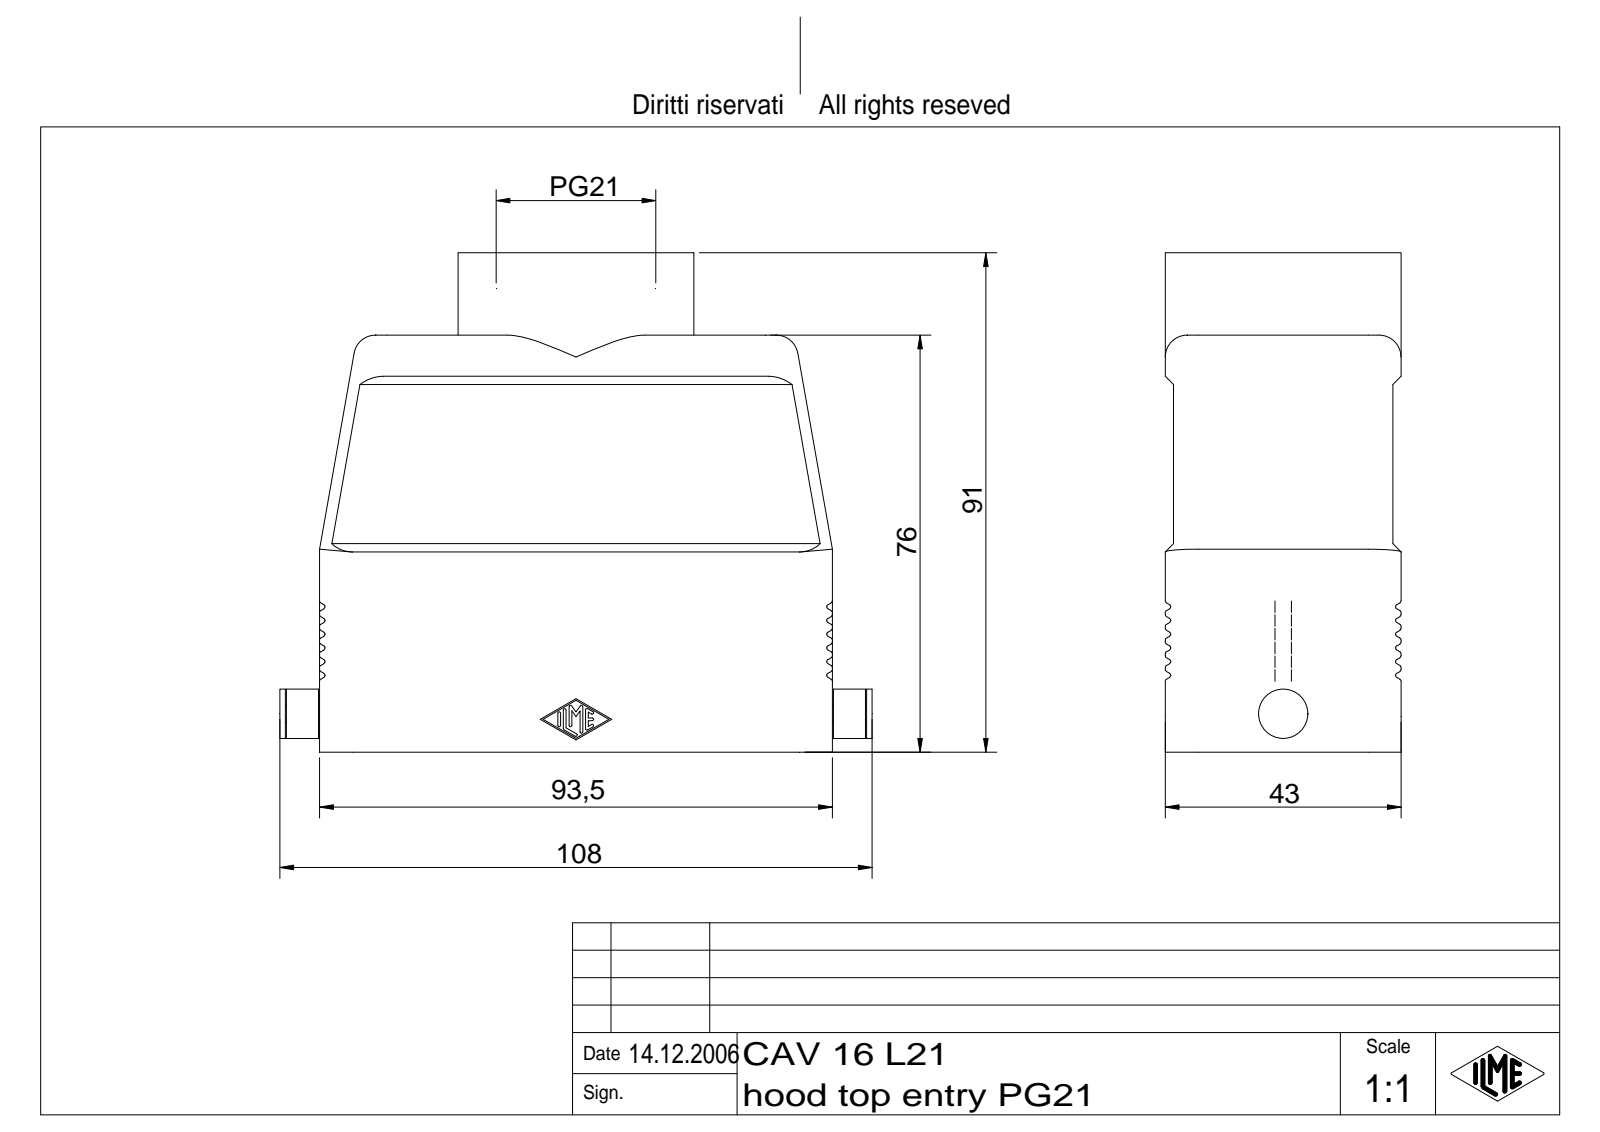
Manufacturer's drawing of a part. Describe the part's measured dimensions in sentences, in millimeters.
The part is named "CAV 16 L21". Its 3-D file was written by "Autodesk Inventor 7 (AUTOMOTIVE_DESIGN)". It is 1 solid with 843 faces: 150 planar, 420 cylindrical and 273 other. Overall it measures 108 by 91 by 43 millimeters. Its volume is 80 749 cubic millimeters and its surface area 49 184 square millimeters. Round holes: 1 of diameter 25, 1 of diameter 26.78. Round bosses or shafts: 1 of diameter 43, 1 of diameter 9, 1 of diameter 3. Partial cylindrical surfaces (rounded edges, fillets, slot ends): 96 of radius 0.4, 14 of radius 0.25, 8 of radius 6, 4 of radius 1.5, 4 of radius 3, 4 of radius 4, 2 of radius 5. The main face-to-face distances are 1.5, 3, 40, 37, 38.5, 41.5, 43, 90.5, 18, 15.
